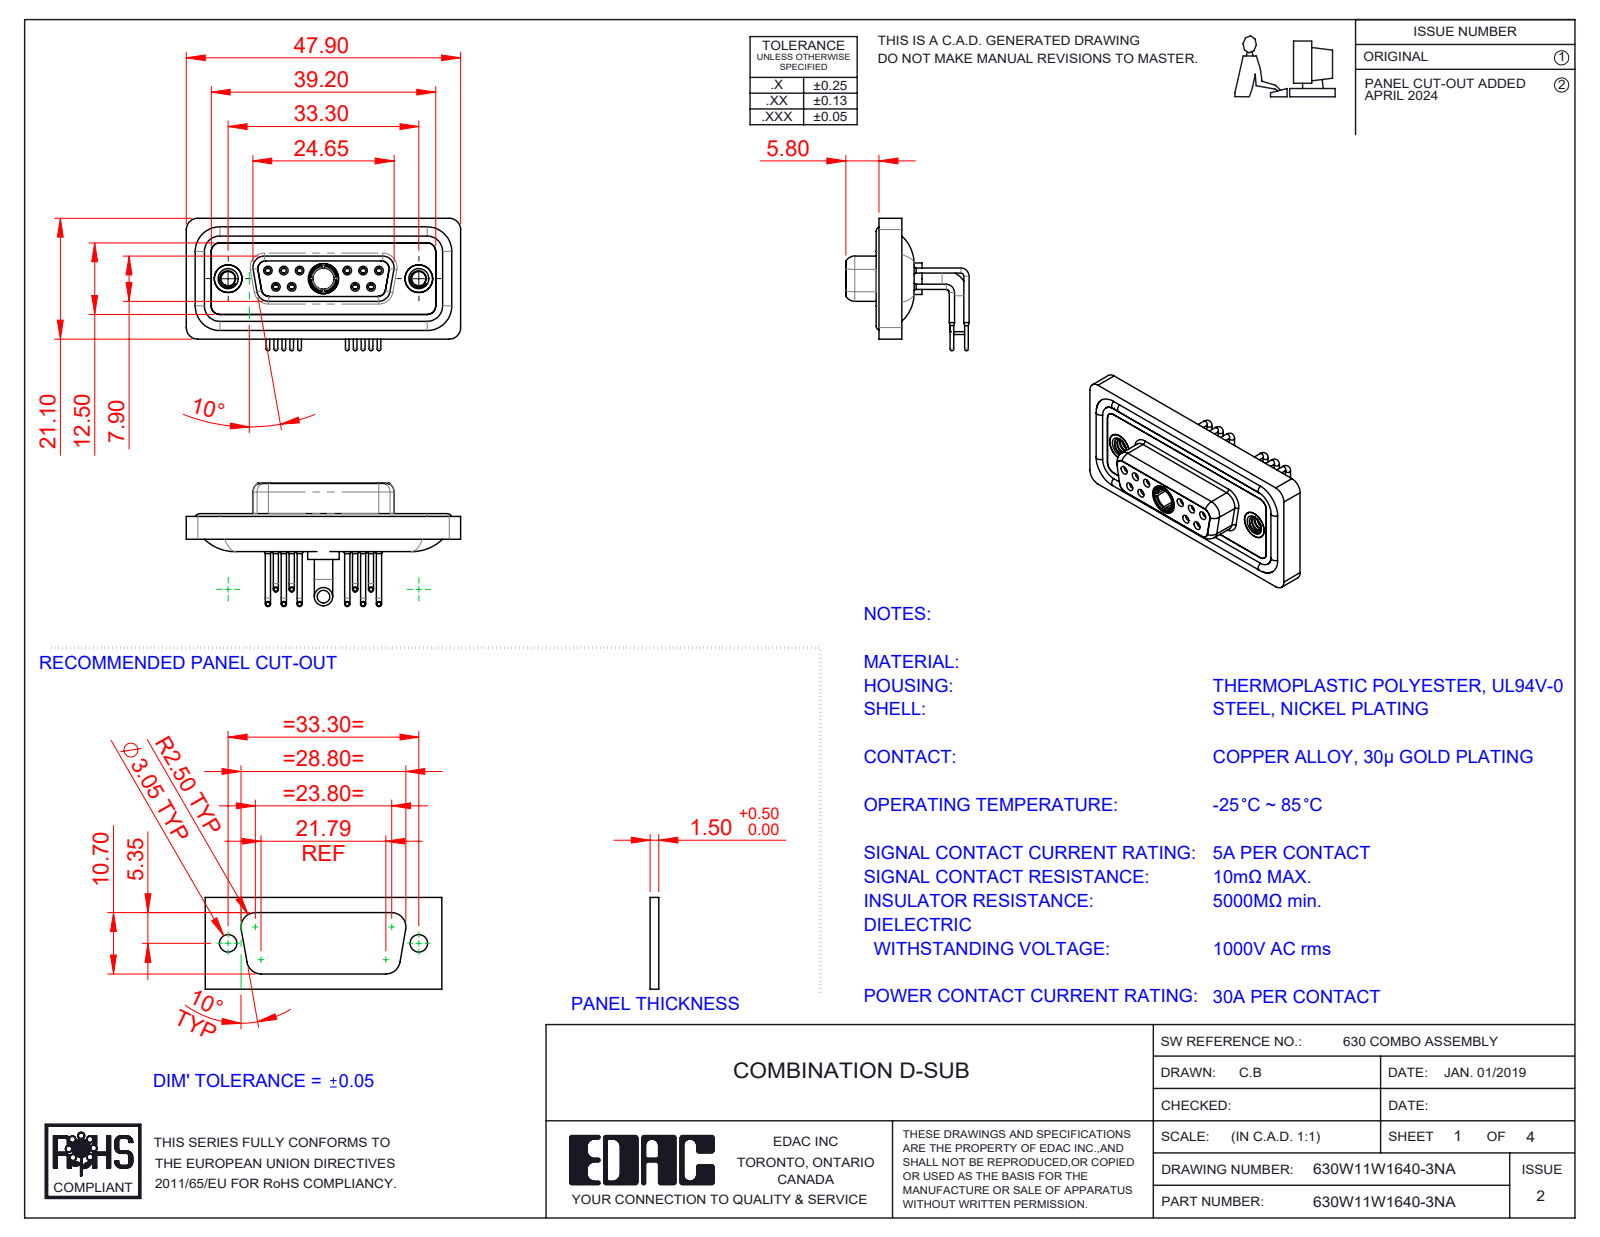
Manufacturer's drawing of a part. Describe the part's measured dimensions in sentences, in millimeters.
The part is named "630Combo Housing_11W1; 630Combo Shell Rear_15 Contacts; Power Socket_30A RA; 630Combo Shell Front_15 Contacts (+5 more)". Its 3-D file was written by "SolidWorks 2023 (CONFIG_CONTROL_DESIGN)". It is 19 solids with 988 faces: 284 planar, 441 cylindrical and 263 other. Overall it measures 47.9 by 23.12 by 21.53 millimeters. Its volume is 6 238 cubic millimeters and its surface area 10 492 square millimeters. Round holes: 10 of diameter 0.9, 10 of diameter 1.1, 10 of diameter 1.5, 10 of diameter 2, 6 of diameter 1.7, 4 of diameter 1.6, 3 of diameter 4.85, 2 of diameter 2.5, 2 of diameter 4, 2 of diameter 4.05, 2 of diameter 5, 1 of diameter 3.7. Round bosses or shafts: 10 of diameter 1.6, 10 of diameter 0.9, 10 of diameter 0.65, 2 of diameter 4.95, 2 of diameter 4.8, 2 of diameter 3.2, 1 of diameter 5.5, 1 of diameter 5.2. Partial cylindrical surfaces (rounded edges, fillets, slot ends): 20 of radius 2, 18 of radius 1.5, 12 of radius 1.35, 8 of radius 1.6, 4 of radius 0.25, 4 of radius 0.5, 4 of radius 0.6, 4 of radius 0.65. The main face-to-face distances are 0.4, 1.8, 1.1, 1.6, 2.5, 2.9, 3.1, 3.7, 4.1, 1.5. The hole center spacings are 3.16, 2.77, 13.85, 11.08, 16.62, 5.03, 5.04, 5.54.
